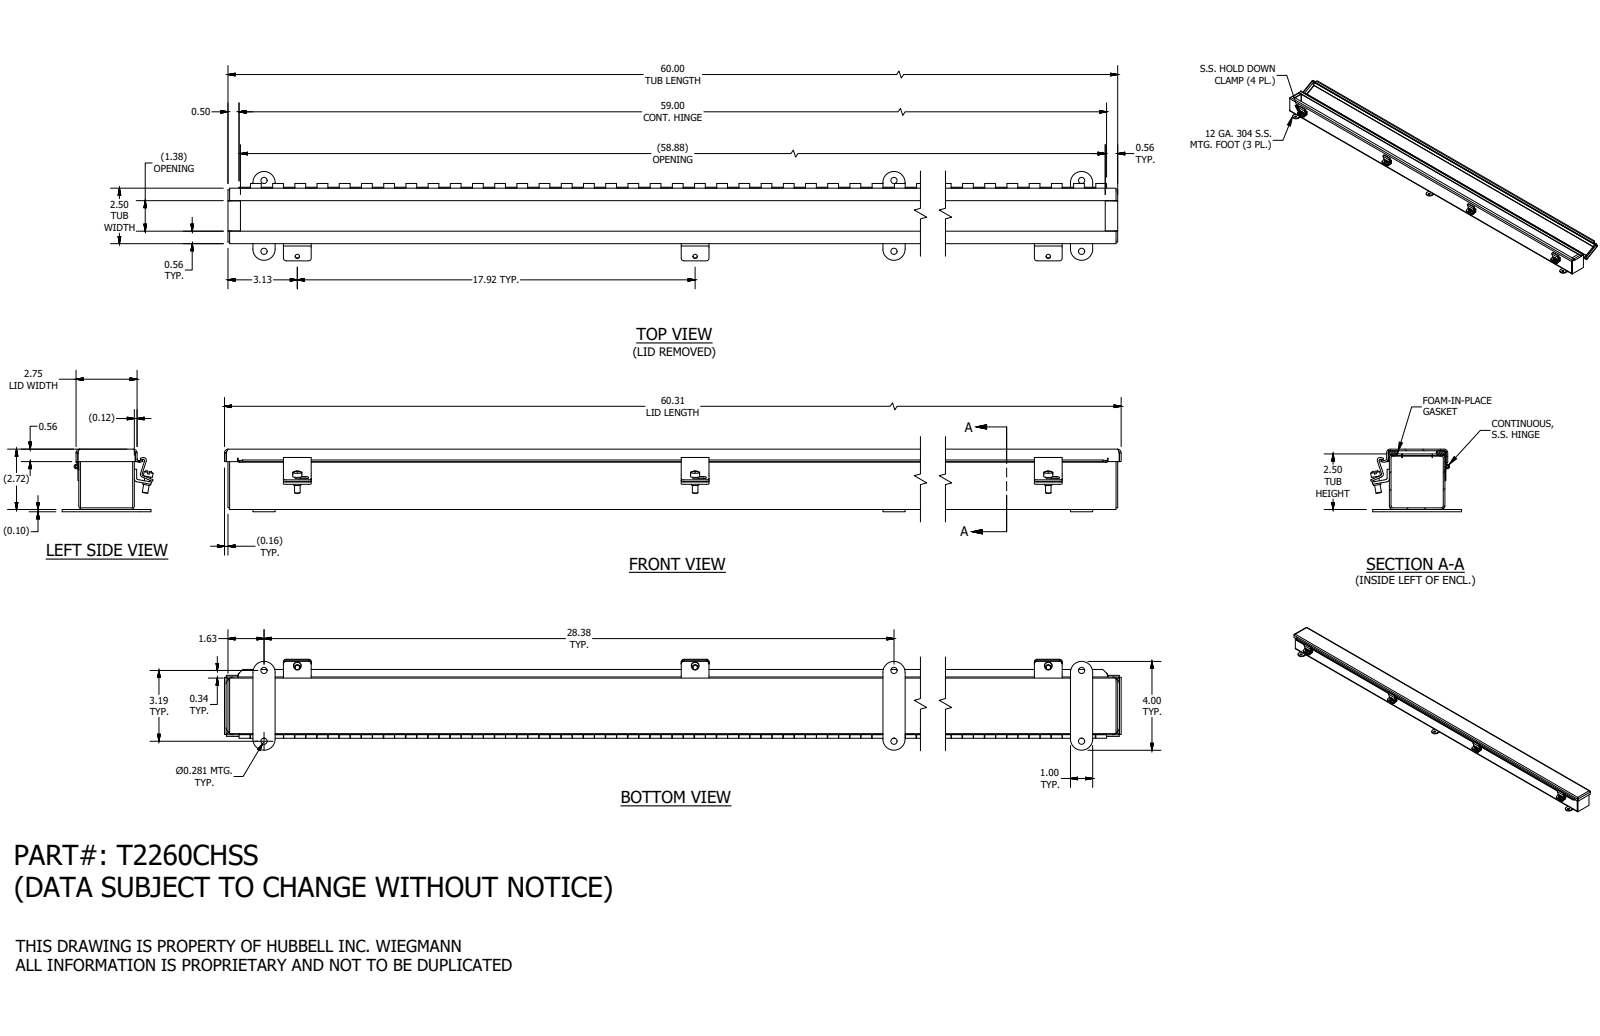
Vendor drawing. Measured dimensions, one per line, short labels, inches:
name: T2260CHSS
written by: SolidWorks 2019 (AUTOMOTIVE_DESIGN)
unit: in
bodies: 23 solids, 1024 faces (613 planar, 365 cylindrical, 46 other)
size: 60.313 × 4.098 × 2.822
volume: 71.91 in³; area: 1 907 in²
holes: 8× ⌀0.11, 6× ⌀0.281, 4× ⌀0.196, 1× ⌀0.116
bosses: 4× ⌀0.41, 4× ⌀0.344, 4× ⌀0.25, 1× ⌀0.2, 1× ⌀0.1
rounds: 16× R0.125, 11× R0.094, 11× R0.168, 8× R0.085, 8× R0.133, 6× R0.5, 4× R0.242, 3× R0.063
face distances: 0.074, 2.426, 2.644, 2.5, 2.352, 2.718, 2.57, 0.218, 2.552, 0.126
hole spacings: 17.917, 0.75, 28.375, 28.553, 35.833, 3.187, 17.167, 17.917
